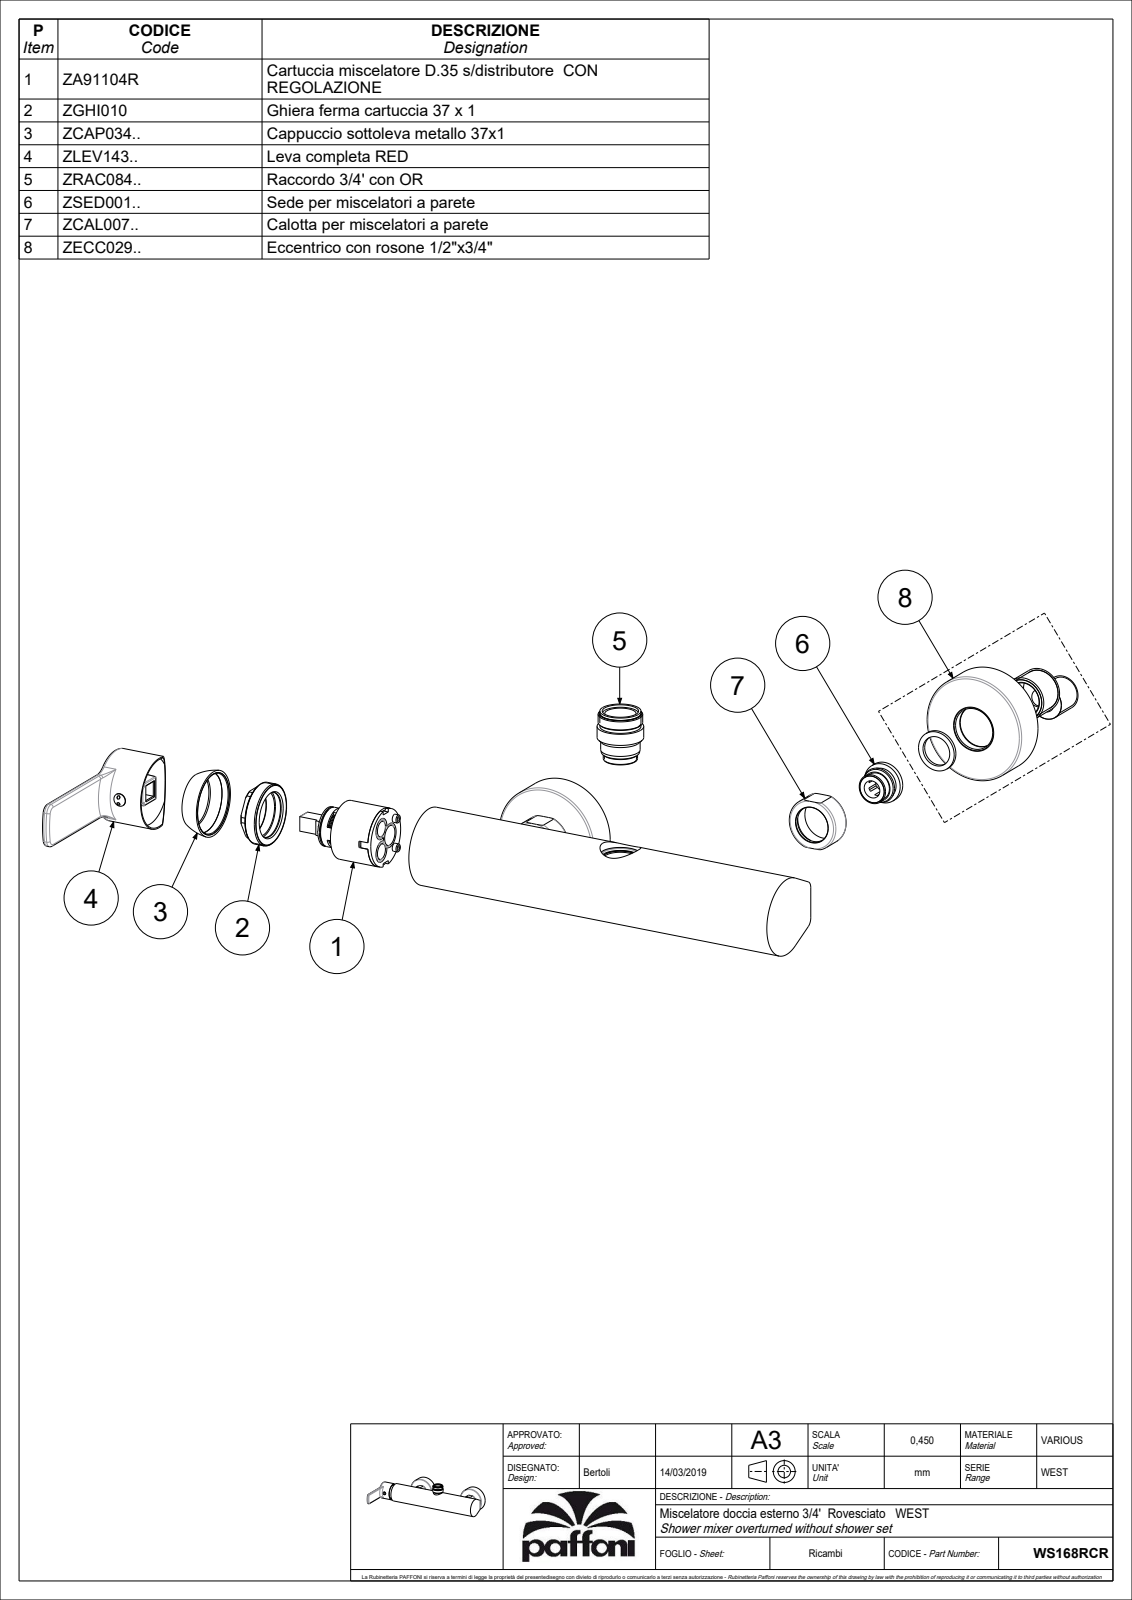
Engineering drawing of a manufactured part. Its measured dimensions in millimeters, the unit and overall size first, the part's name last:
Units: millimetres
Overall size (bounding box): 277.83 × 148 × 74.2
Round holes (diameter × count): ⌀7 ×3, ⌀10.5 ×3, ⌀3.3 ×2, ⌀4 ×2, ⌀18 ×2, ⌀21.6 ×2, ⌀24.5 ×2, ⌀25 ×2, ⌀62.3 ×2, ⌀3 ×1, ⌀3.5 ×1, ⌀4.5 ×1
Round bosses / shafts (diameter × count): ⌀24 ×3, ⌀63.5 ×2, ⌀27 ×2, ⌀23 ×2, ⌀18.5 ×2, ⌀17.7 ×2, ⌀43 ×1, ⌀35.5 ×1
Partial cylindrical surfaces — rounded edges, fillets, slot ends (radius × count): R0.5 ×66, R1.5 ×48, R0.15 ×11, R0.3 ×4, R5 ×4, R1 ×2, R1.3 ×2, R10 ×2
Main face-to-face distances: 3.7, 0.6, 29.8, 29.2, 3.5, 15, 14.2, 26.3, 25.7, 10.5
Hole centre spacings: 7.07, 8.6, 11.4, 4, 6, 10, 12.5, 14
Volume: 265 763 mm³ · Surface area: 164 529 mm²
Bodies: 1 solid, 1558 faces (754 planar, 439 cylindrical, 365 other)
Part name (STEP PRODUCT): WS168RCR
STEP written by: CREO PARAMETRIC BY PTC INC, 2020044 (CONFIG_CONTROL_DESIGN)
